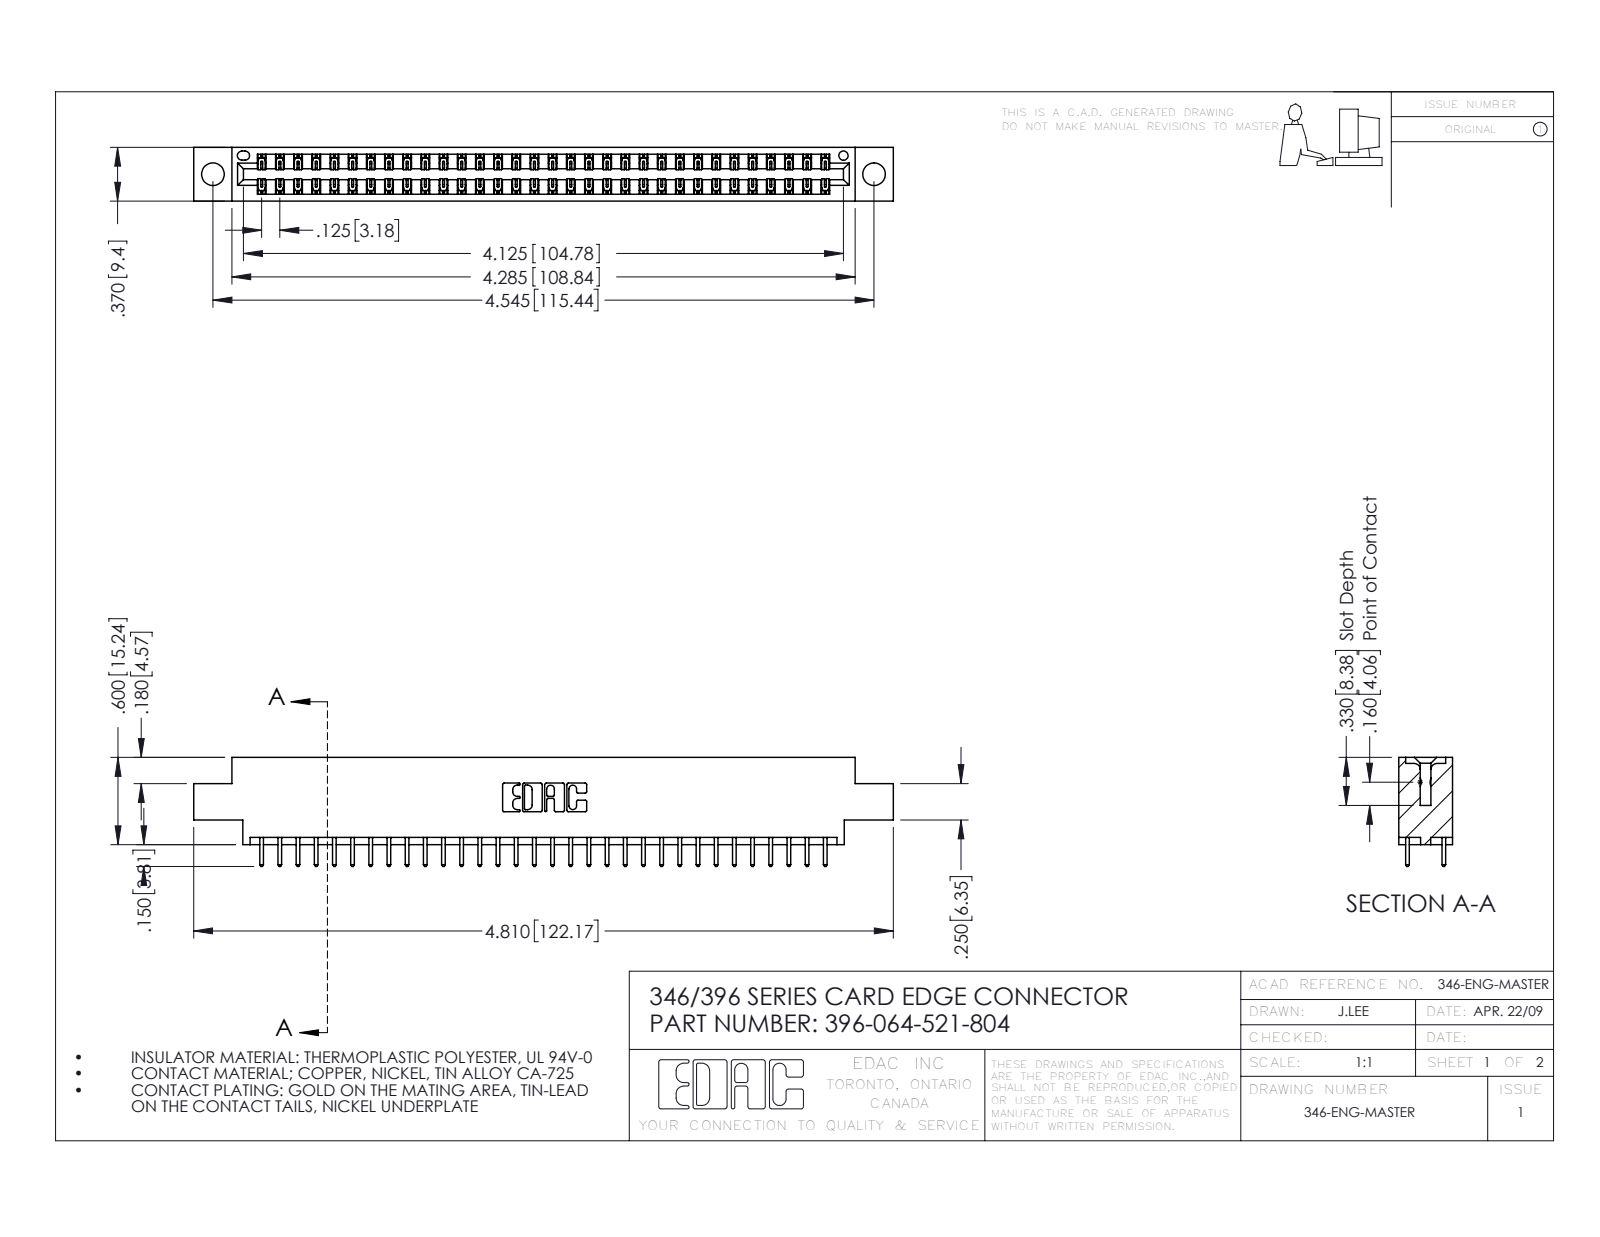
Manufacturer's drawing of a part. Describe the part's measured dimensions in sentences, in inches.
The part is named "346 Part_0.170 Offset - 0.156 Dia-TH; 345-292-001_345-293-121; 396-064-521-804". Its 3-D file was written by "SolidWorks 2016 (CONFIG_CONTROL_DESIGN)". It is 65 solids with 3454 faces: 2320 planar, 1134 cylindrical and 0 other. Overall it measures 4.81 by 0.75 by 0.37 inches. Its volume is 0.706 cubic inches and its surface area 24.12 square inches. Round holes: 2 of diameter 0.156, 1 of diameter 0.064. Partial cylindrical surfaces (rounded edges, fillets, slot ends): 96 of radius 0.006, 64 of radius 0.01, 22 of radius 0.01, 6 of radius 0.007, 6 of radius 0.031, 3 of radius 0.026, 2 of radius 0.014, 2 of radius 0.022. The main face-to-face distances are 0.048, 0.322, 0.37, 0.25, 0.072, 0.298, 0.025, 0.275, 0.148, 0.222. The hole center spacings are 0.246, 4.337, 4.545.
